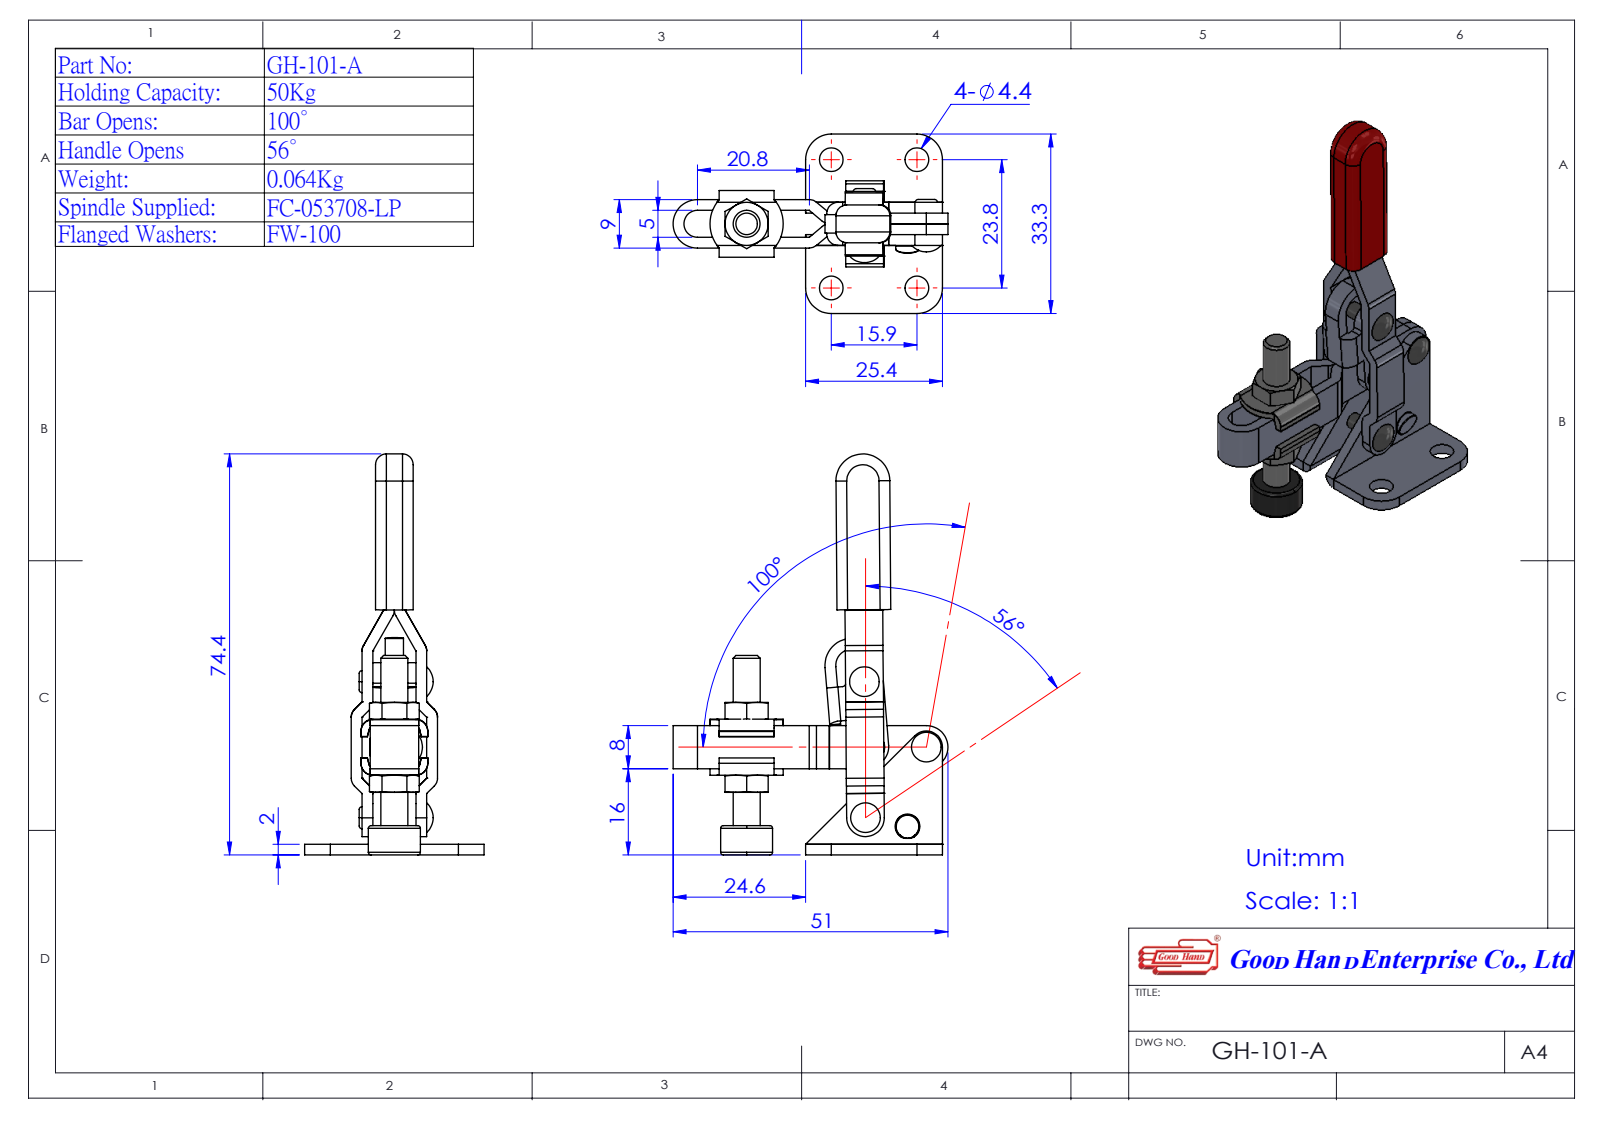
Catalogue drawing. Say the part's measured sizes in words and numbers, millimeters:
The part is named "Group4^493778(GH-101-A); Group2^493778(GH-101-A); Group1^493778(GH-101-A); 493778(GH-101-A) (+2 more)". Its 3-D file was written by "SolidWorks 2016 (AUTOMOTIVE_DESIGN)". It is 5 solids with 369 faces: 198 planar, 111 cylindrical and 60 other. Overall it measures 74.4 by 51 by 33.3 millimeters. Its volume is 9 744 cubic millimeters and its surface area 10 484 square millimeters. Round holes: 4 of diameter 2.5, 4 of diameter 4.4, 1 of diameter 3.05. Round bosses or shafts: 2 of diameter 3.05, 1 of diameter 9.65, 1 of diameter 5, 1 of diameter 3. Partial cylindrical surfaces (rounded edges, fillets, slot ends): 6 of radius 1, 5 of radius 0.1, 5 of radius 2.2, 4 of radius 4.75, 3 of radius 3.5, 2 of radius 2.01, 2 of radius 2.1, 1 of radius 0.6. The main face-to-face distances are 2, 6, 1.5, 8, 0.5, 4, 8.5, 7, 5.5, 1. The hole center spacings are 15.9, 23.8, 28.62, 10.5, 12.2, 13.11, 16.74, 17.29.
